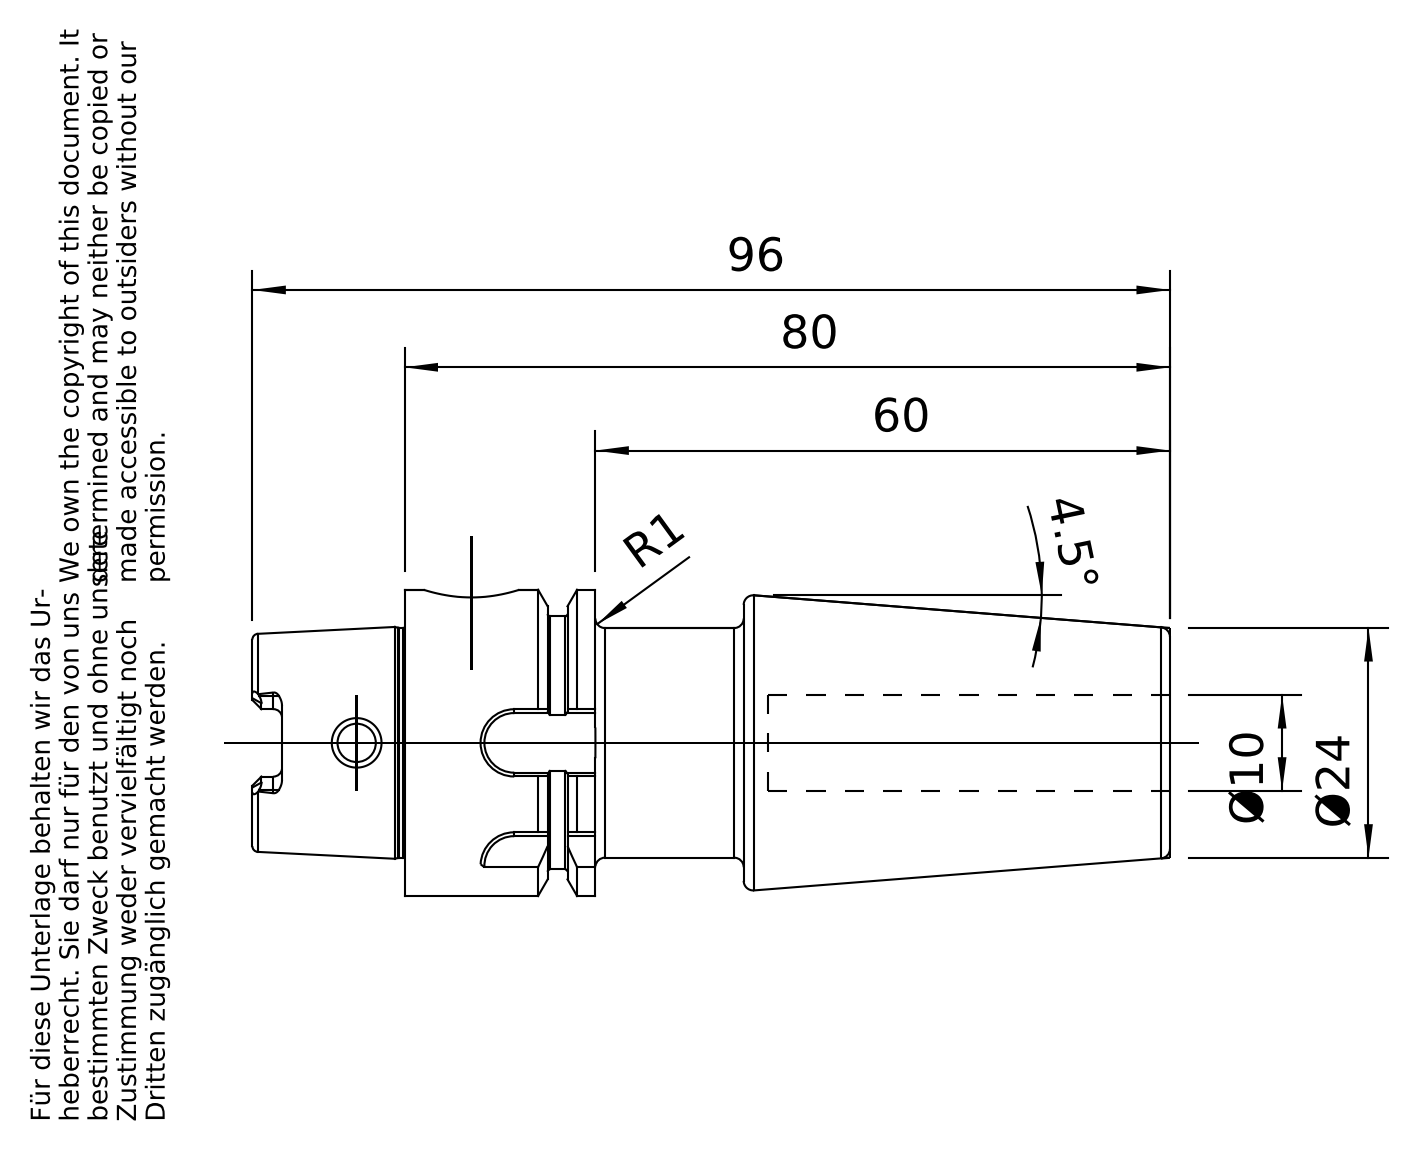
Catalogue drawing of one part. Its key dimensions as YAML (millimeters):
part_name: "A32-140-10"
step_written_by: "PRO/ENGINEER BY PARAMETRIC TECHNOLOGY CORPORATION, 2010430 (CONFIG_CONTROL_DESIGN)"
units: millimeters
bodies: {solids: 1, faces: 188, planar: 63, cylindrical: 49, other: 76}
overall_size: [95.9, 32, 32]
volume: 44629
surface_area: 13357
round_holes:
  - {diameter: 10, count: 2}
  - {diameter: 4, count: 1}
  - {diameter: 8.5, count: 1}
  - {diameter: 10.22, count: 1}
  - {diameter: 10.5, count: 1}
  - {diameter: 17.04, count: 1}
  - {diameter: 21.07, count: 1}
round_bosses_or_shafts:
  - {diameter: 32, count: 1}
  - {diameter: 26.45, count: 1}
  - {diameter: 24.03, count: 1}
  - {diameter: 24, count: 1}
partial_cylinders:
  - {radius: 0.9, count: 6}
  - {radius: 1.38, count: 4}
  - {radius: 3.5, count: 3}
  - {radius: 3.51, count: 1}
face_to_face_distances: [80, 19.95, 60.05, 6, 7.95, 12, 72.05, 35.45, 27.5, 15.5]
